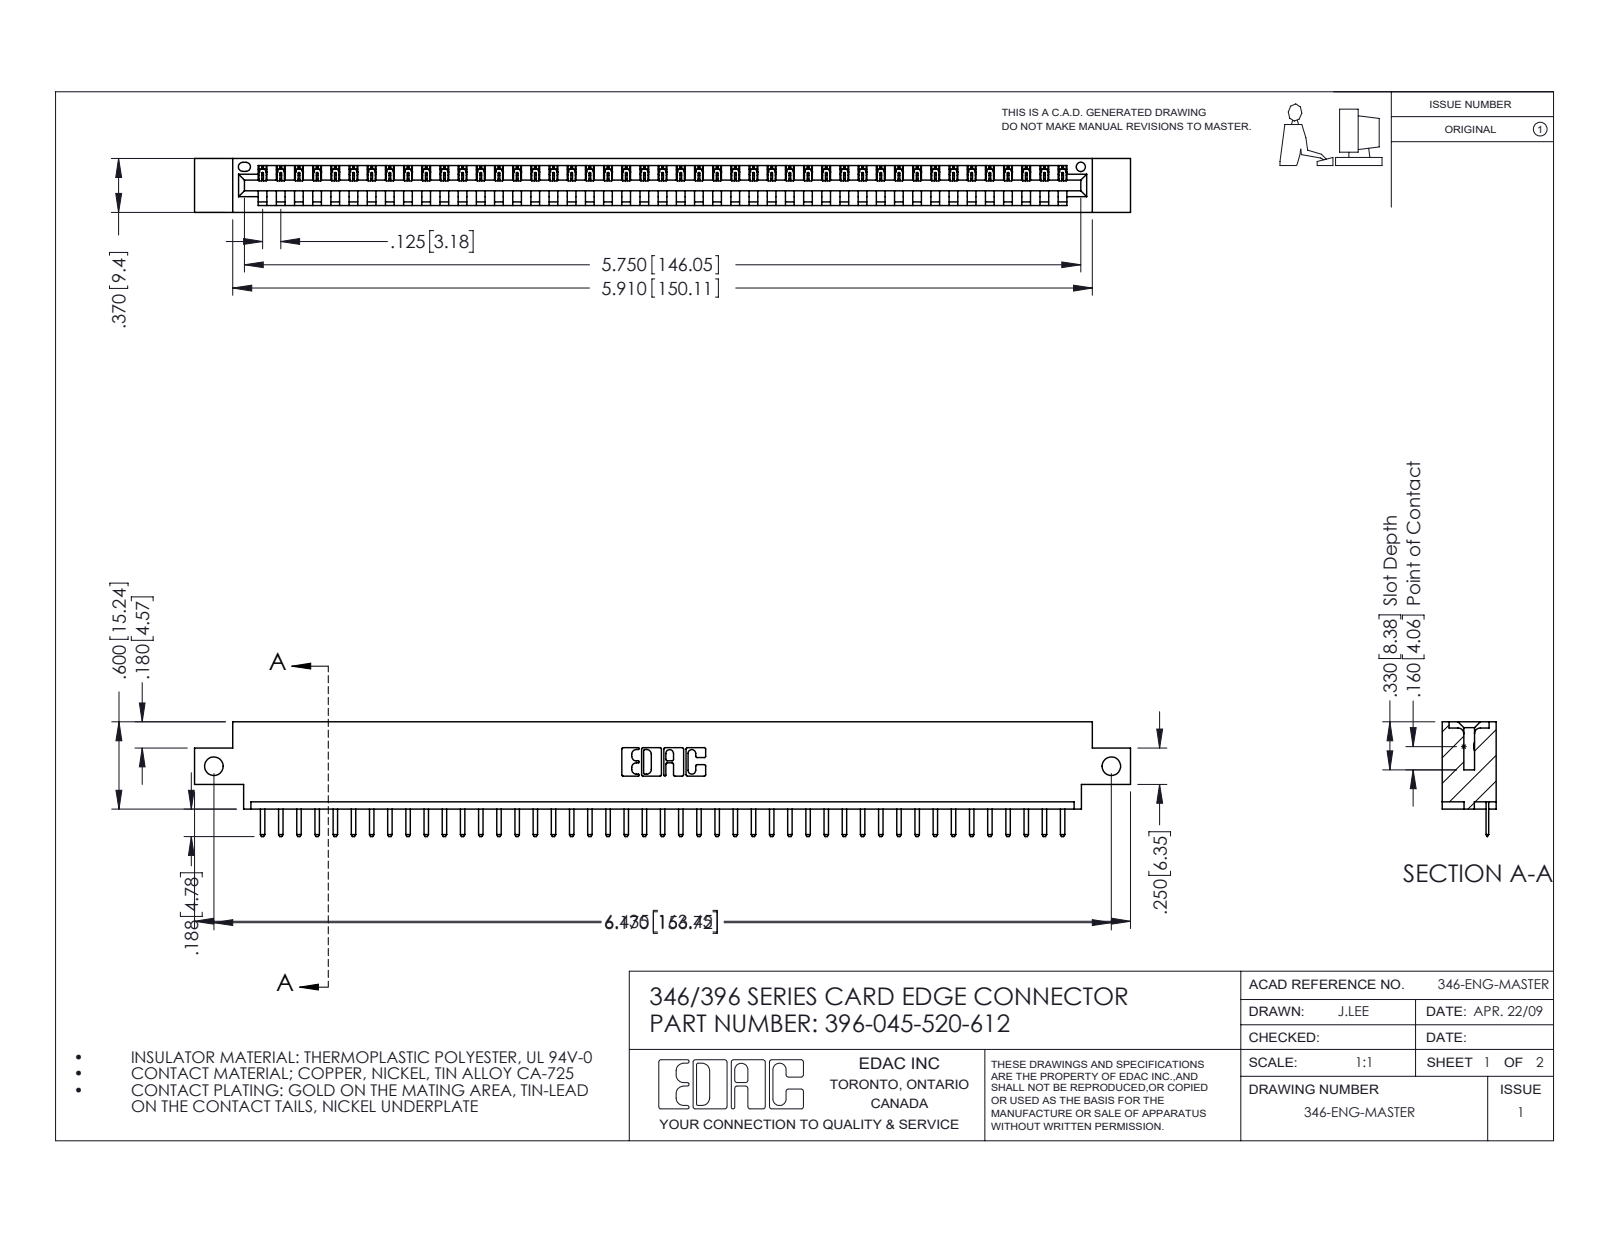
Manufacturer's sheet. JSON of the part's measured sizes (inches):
{"part_name": "396-045-520-612; 345-292-001_345-293-120; 346 Part_0.170 Offset - Side Mount", "step_written_by": "SolidWorks 2016 (CONFIG_CONTROL_DESIGN)", "units": "inches", "bodies": {"solids": 46, "faces": 2916, "planar": 1970, "cylindrical": 946, "other": 0}, "overall_size": [6.435, 0.788, 0.37], "volume_in3": 0.933, "surface_area_in2": 29.03, "round_holes": [[0.128, 2], [0.064, 1]], "partial_cylinders_radius": [[0.01, 92], [0.006, 90], [0.01, 22], [0.007, 6], [0.031, 6], [0.026, 3], [0.031, 2], [0.04, 2]], "face_to_face_distances": [0.048, 0.322, 0.37, 0.25, 0.148, 0.222, 0.1, 0.174, 0.072, 0.298], "hole_center_spacings": [6.17]}
